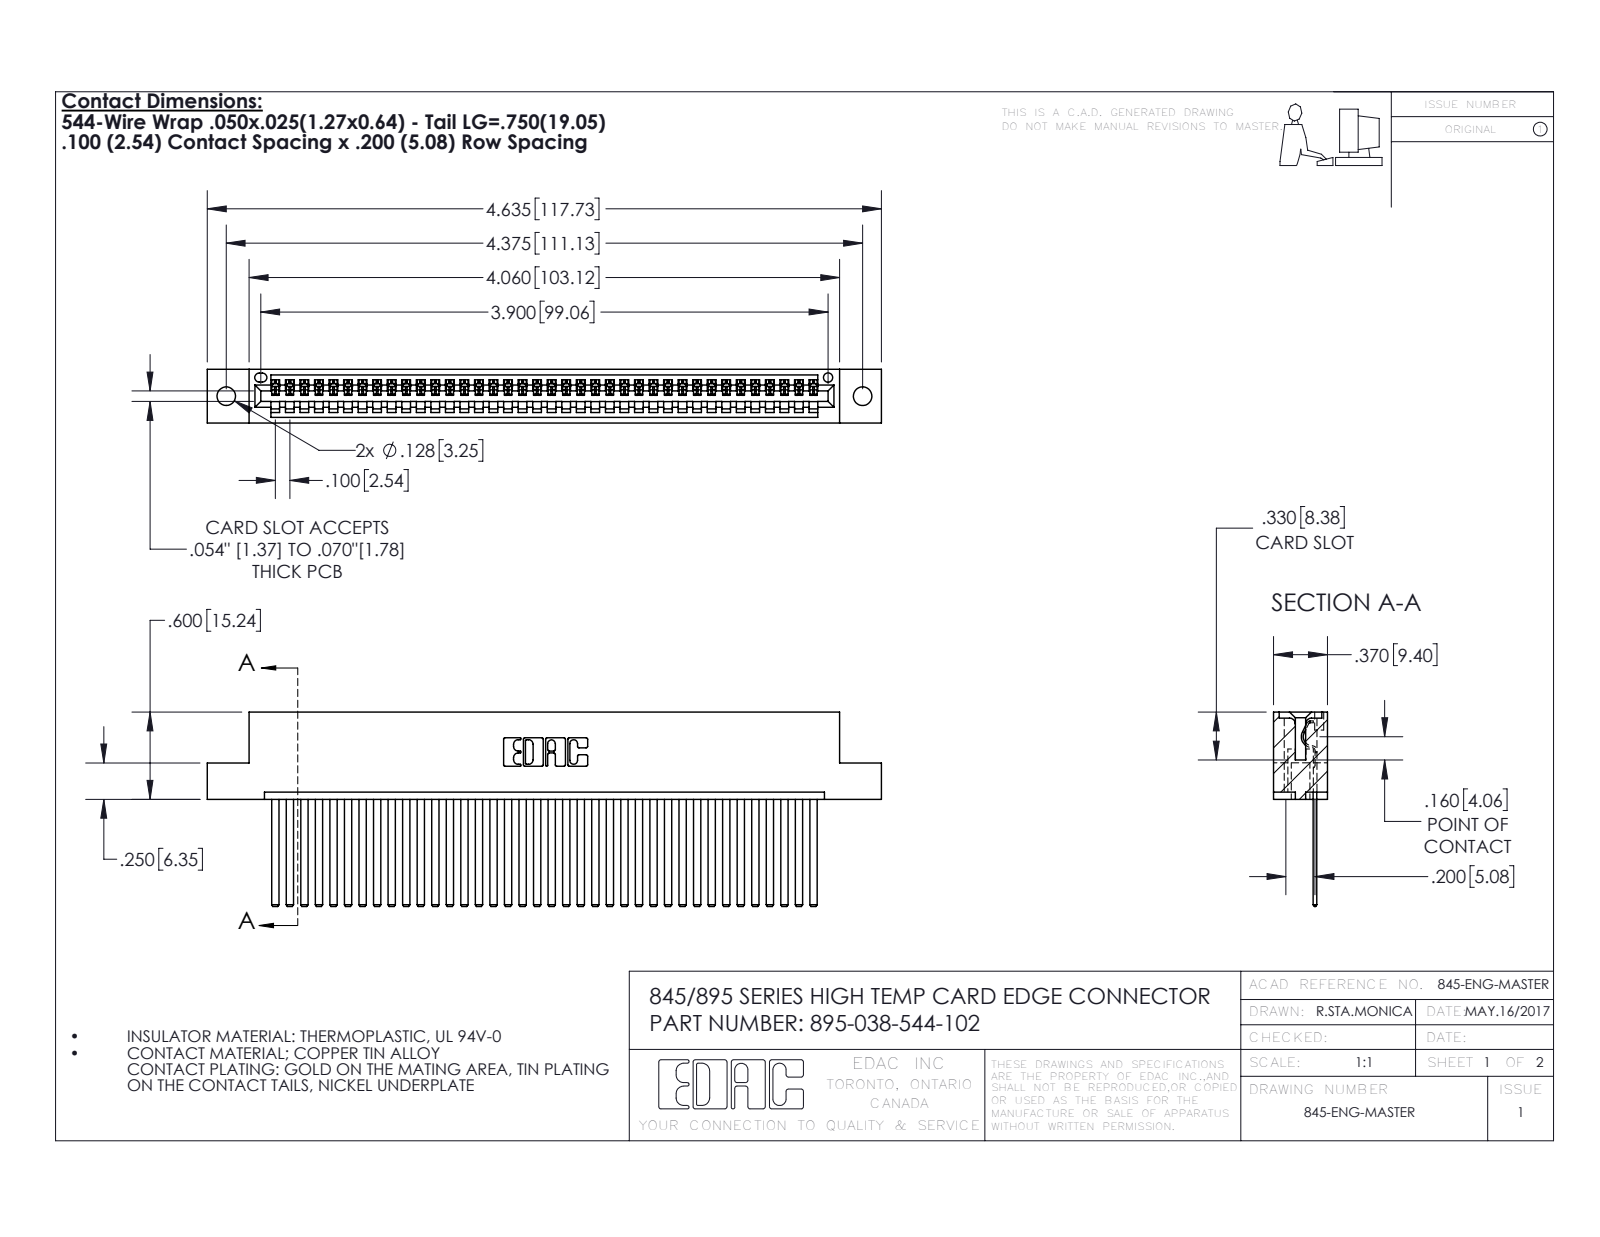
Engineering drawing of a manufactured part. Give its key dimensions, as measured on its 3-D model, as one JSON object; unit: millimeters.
{"part_name": "345 Part_Flush Mounting Lugs - 0.128 Dia; 345-292-001_345-293-144; 395-038-544-102", "step_written_by": "SolidWorks 2016 (CONFIG_CONTROL_DESIGN)", "units": "millimeters", "bodies": {"solids": 39, "faces": 2102, "planar": 1448, "cylindrical": 654, "other": 0}, "overall_size": [117.7, 34, 9.4], "volume_mm3": 11600, "surface_area_mm2": 16350, "round_holes": [[3.3, 2], [1.6, 1]], "partial_cylinders_radius": [[0.2, 76], [0.3, 22], [0.2, 6], [0.8, 6], [0.7, 3], [0.8, 2], [1, 2], [0.4, 1]], "face_to_face_distances": [1.8, 7.6, 0.6, 2.5, 6.9, 5.1, 9.4, 5.7, 3.8, 1.8], "hole_center_spacings": [6.9, 105.1, 111.1]}
